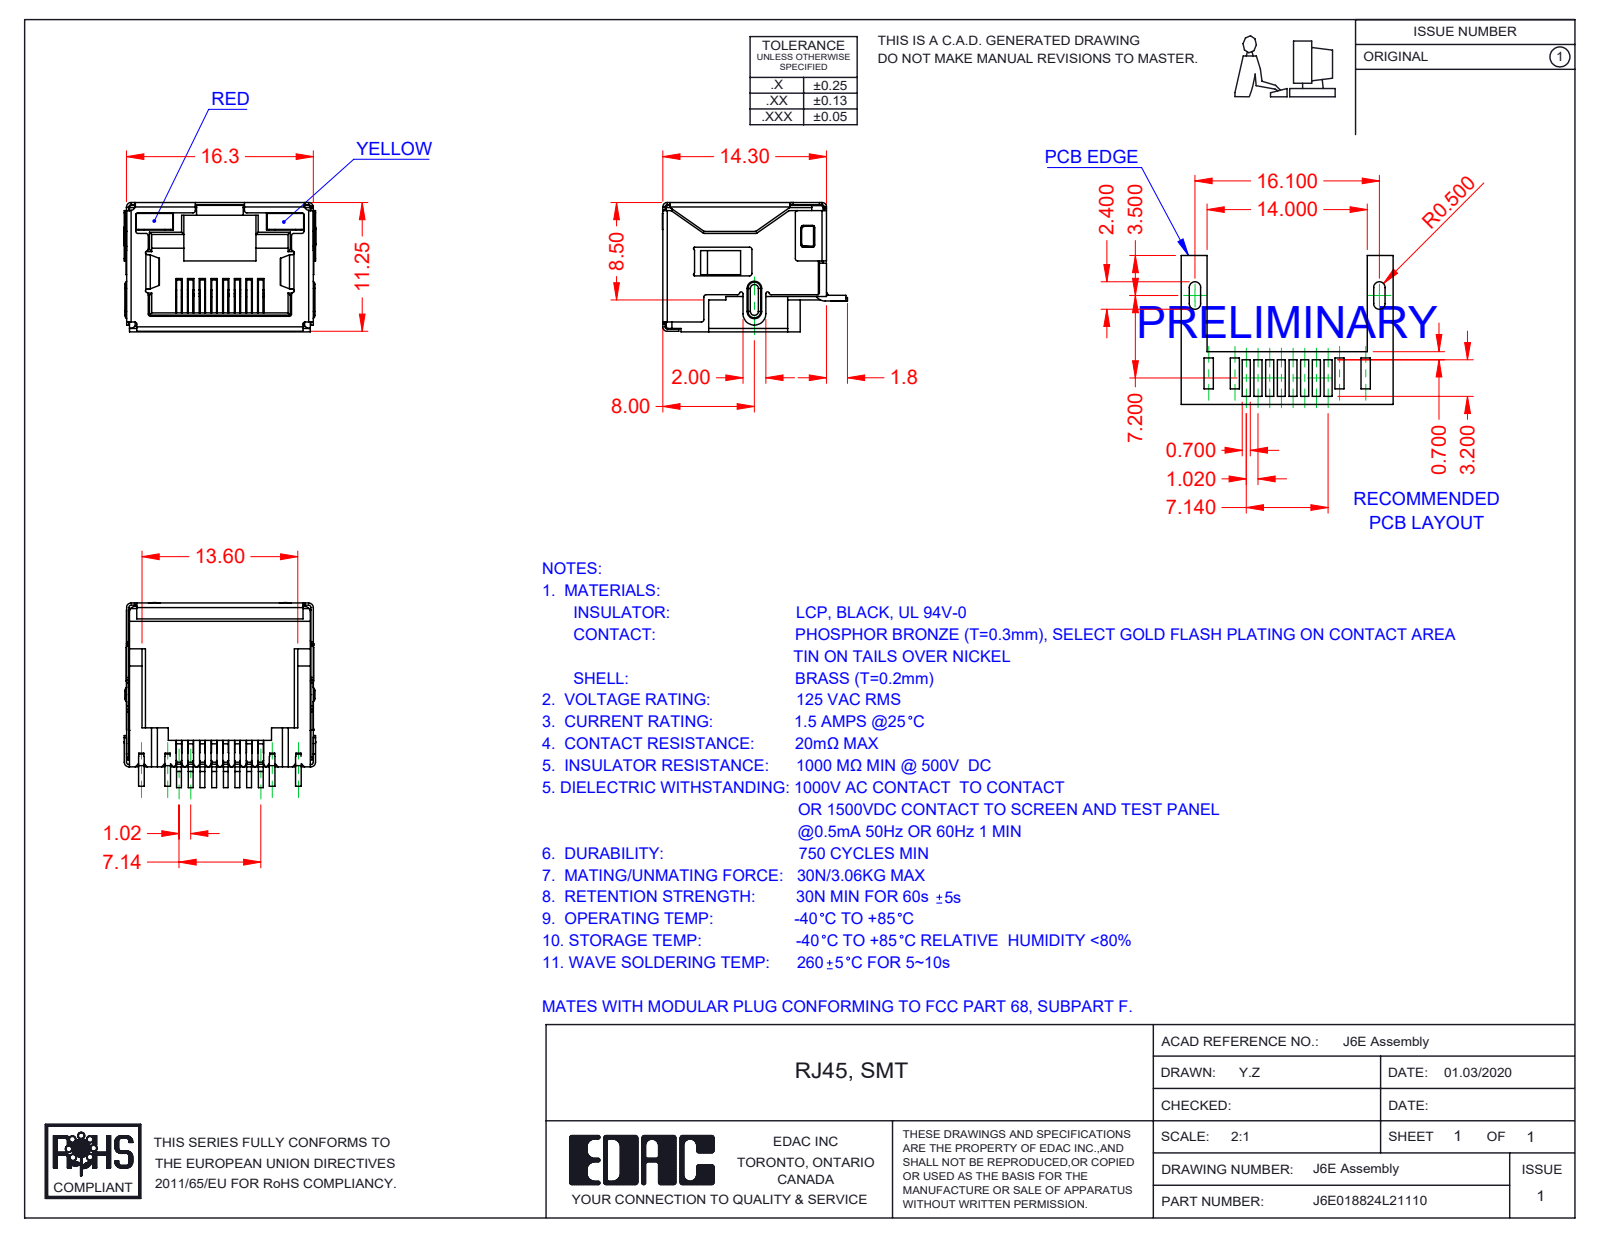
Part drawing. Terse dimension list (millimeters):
name: 6E Insulator_LED; J6E018824L21110; 6E LED RH_1-Yellow; 6E LED LH_2-Red (+2 more)
written by: SolidWorks 2016 (CONFIG_CONTROL_DESIGN)
unit: mm
bodies: 12 solids, 1496 faces (1099 planar, 347 cylindrical, 50 other)
size: 16.75 × 16.15 × 11.3
volume: 1 109 mm³; area: 4 045 mm²
rounds: 82× R0.2, 17× R0.25, 13× R0.4, 13× R0.5, 10× R0.1, 7× R0.15, 4× R0.3, 3× R1
face distances: 11.05, 16.05, 16.1, 15.85, 11.1, 11.3, 2.4, 0.7, 9.85, 0.49
